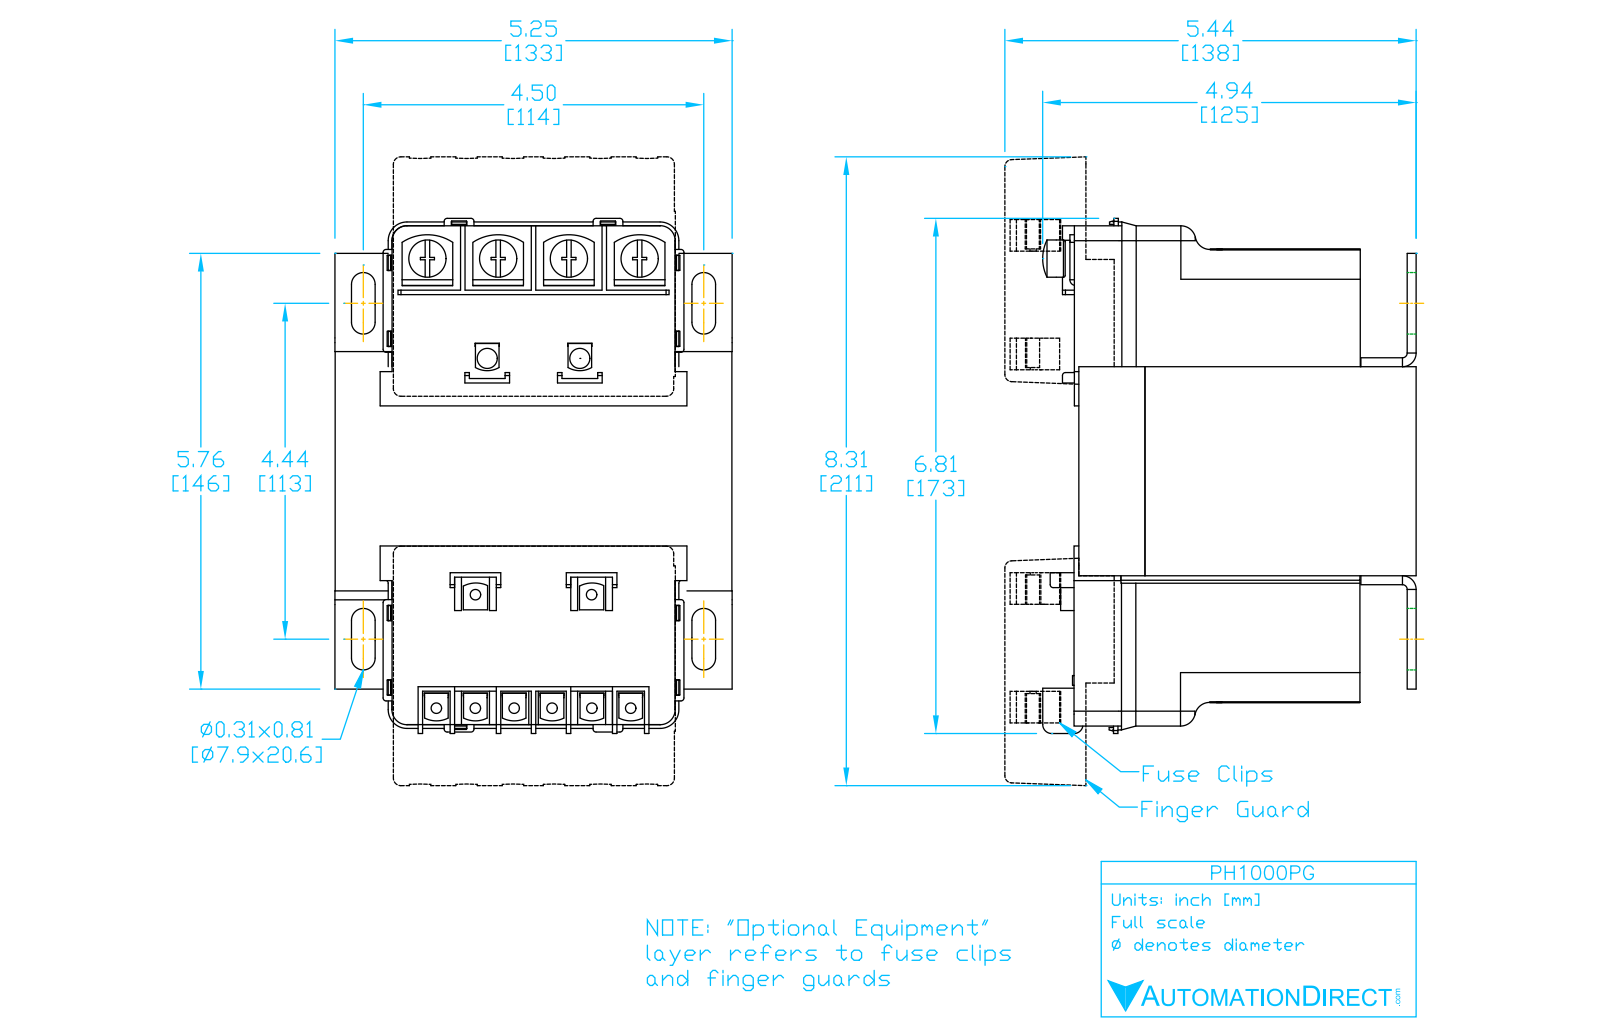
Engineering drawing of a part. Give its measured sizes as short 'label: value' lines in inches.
name: PH1000PG
written by: SolidWorks 2017 (AUTOMOTIVE_DESIGN)
unit: in
bodies: 7 solids, 676 faces (390 planar, 196 cylindrical, 90 other)
size: 6.767 × 5.25 × 4.847
volume: 121.2 in³; area: 313.4 in²
holes: 2× ⌀0.157
rounds: 94× R0.039, 10× R0.197, 4× R0.1, 4× R0.156, 4× R0.248, 4× R0.394, 2× R0.157, 1× R0.062
face distances: 3.15, 0.318, 3.496, 3.814, 4.37, 0.874, 0.556, 0.752, 4.492, 4.847
hole spacings: 3.543
